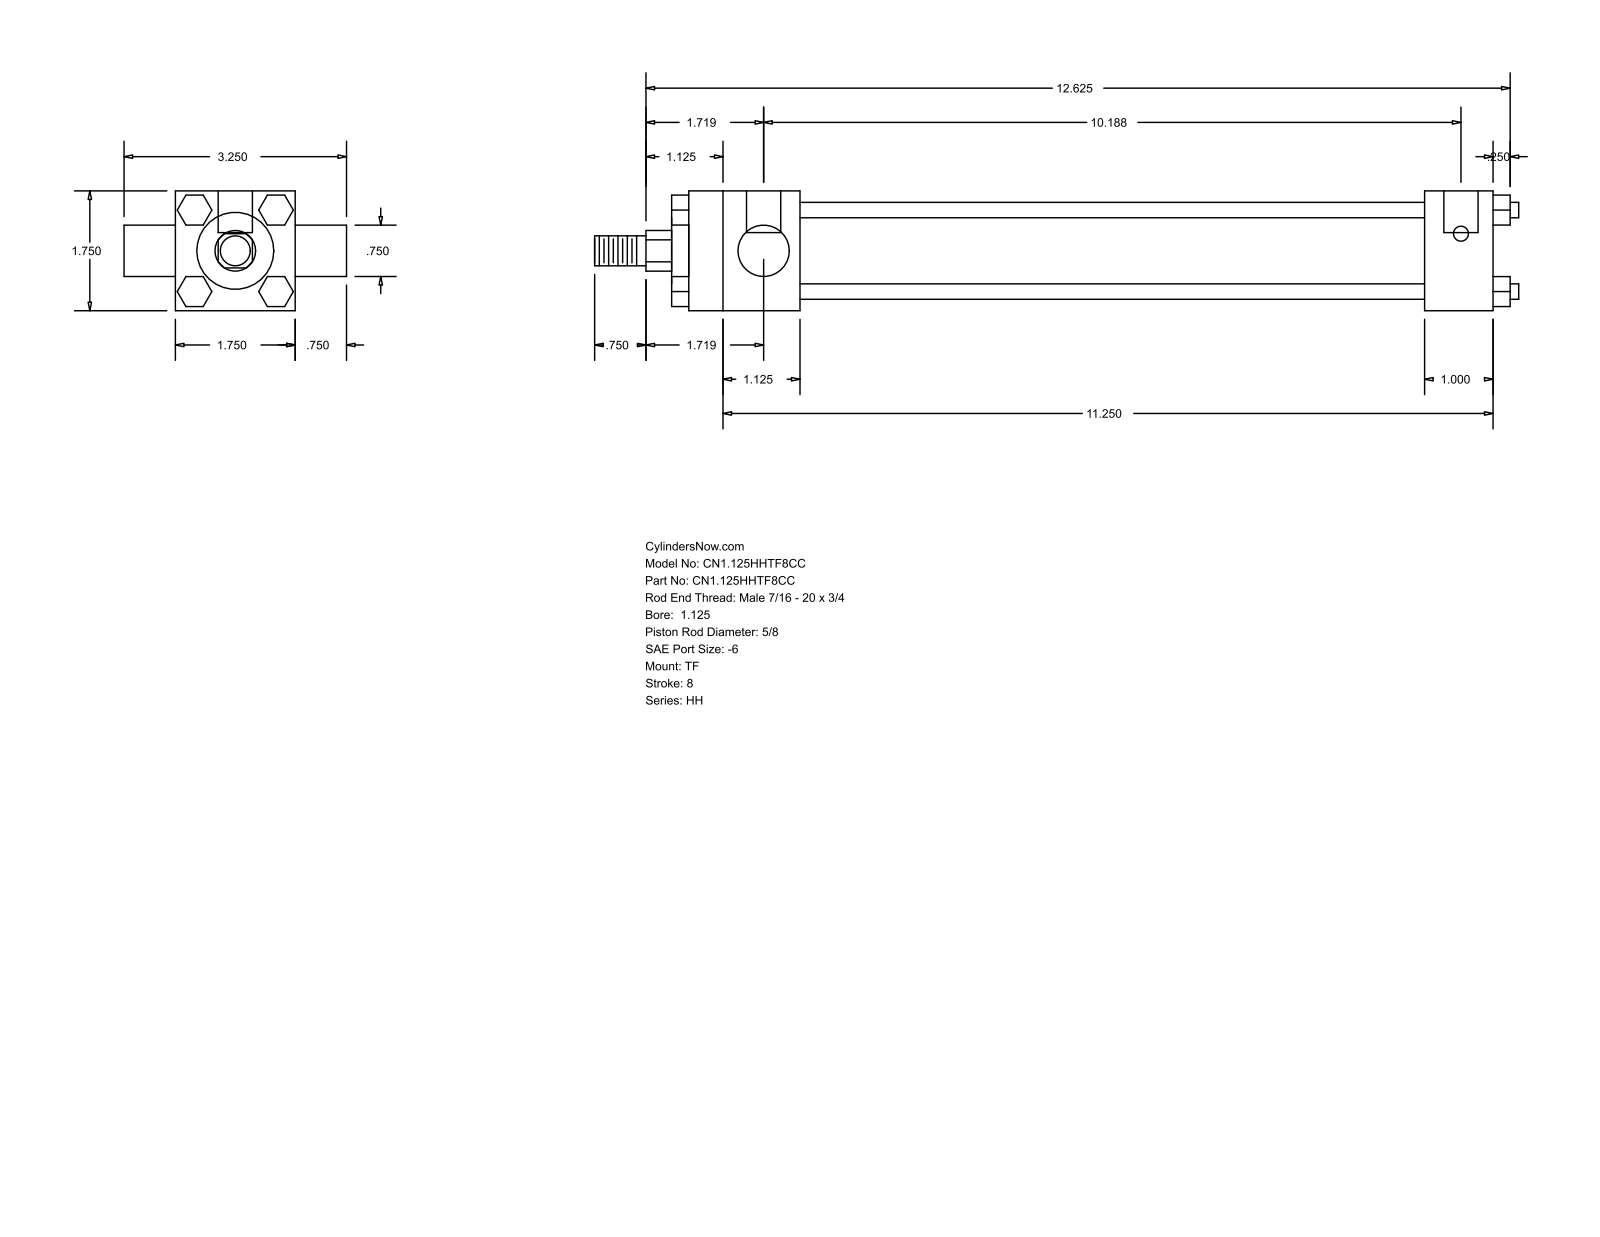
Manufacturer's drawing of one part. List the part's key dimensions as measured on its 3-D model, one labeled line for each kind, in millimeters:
Part name (STEP PRODUCT): HH_TF__0112_0.625
STEP written by: GSSL Pune (CONFIG_CONTROL_DESIGN)
Units: millimetres
Bodies: 0 solids, 120 faces (92 planar, 28 cylindrical, 0 other)
Overall size (bounding box): 342.9 × 82.55 × 44.45
Round holes (diameter × count): ⌀5.56 ×3, ⌀12.7 ×2
Round bosses / shafts (diameter × count): ⌀5.71 ×4, ⌀34.92 ×1, ⌀28.57 ×1, ⌀19.05 ×1, ⌀15.88 ×1, ⌀11.11 ×1
Partial cylindrical surfaces — rounded edges, fillets, slot ends (radius × count): R7.54 ×1
Main face-to-face distances: 44.46, 11.11, 231.78, 257.17, 25.39, 41.27, 273.05, 298.44, 47.62, 6.35
Hole centre spacings: 3.17, 255.59, 258.76
